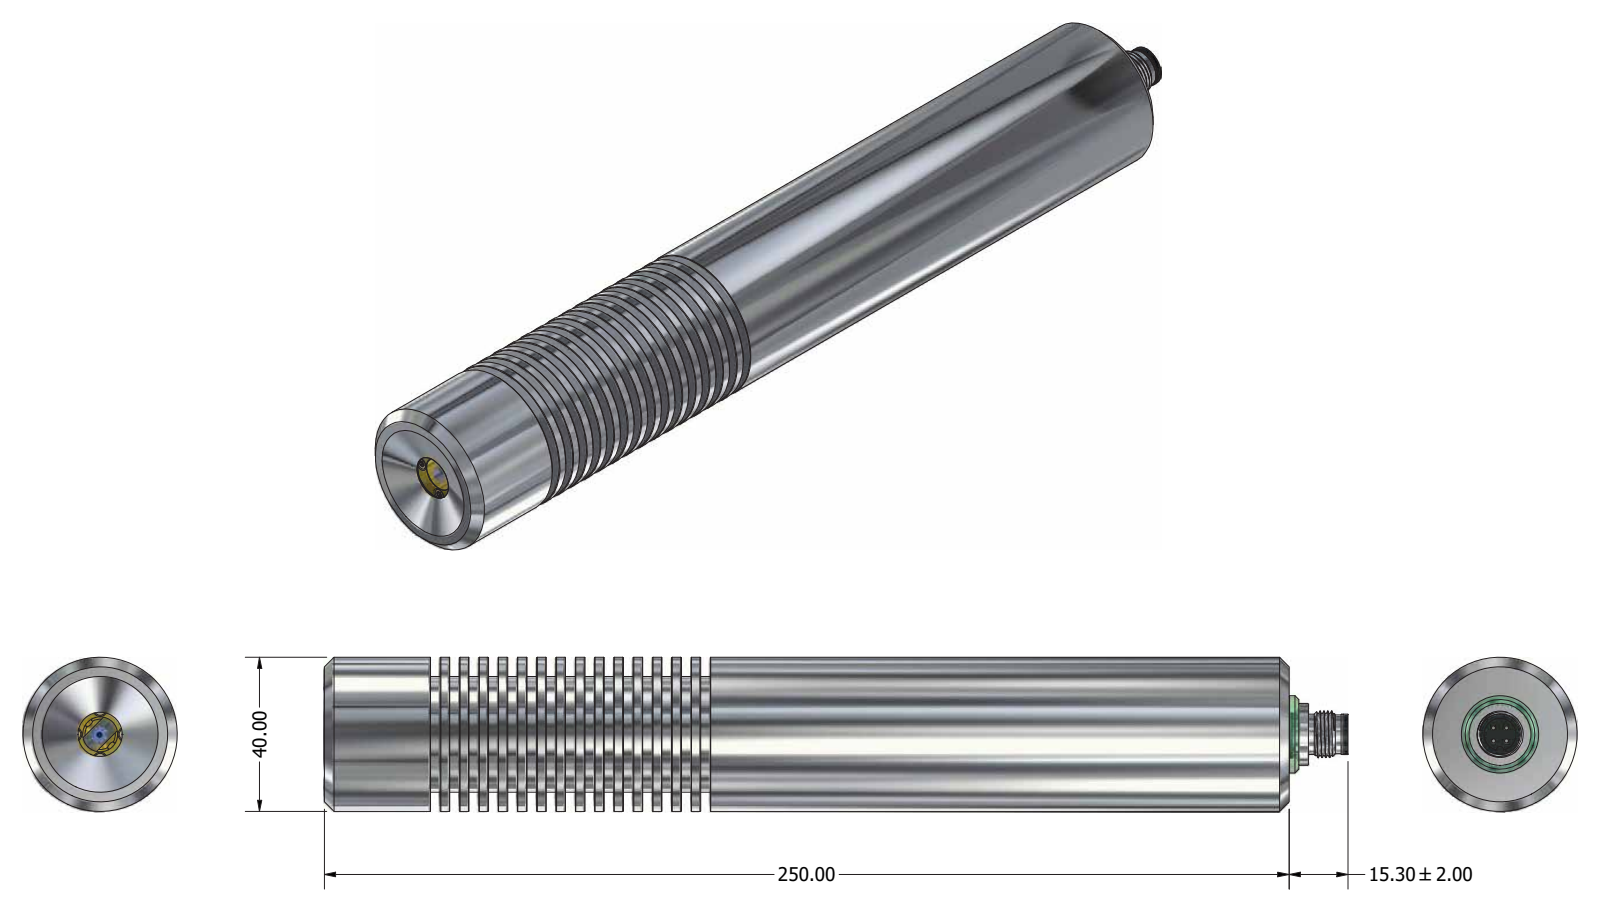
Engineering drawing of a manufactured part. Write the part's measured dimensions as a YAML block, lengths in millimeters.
part_name: "lwpro40; back_40mm_heatsink_rev2; front_40mm_heatsink_rev2; m12_4p_realthread (+1 more)"
step_written_by: "unknown (AUTOMOTIVE_DESIGN)"
units: millimeters
bodies: {solids: 4, faces: 205, planar: 50, cylindrical: 76, other: 79}
overall_size: [265.3, 40, 40]
volume: 242918
surface_area: 64924
round_holes:
  - {diameter: 0.75, count: 4}
  - {diameter: 8.2, count: 1}
  - {diameter: 10.92, count: 1}
  - {diameter: 11.5, count: 1}
  - {diameter: 16, count: 1}
  - {diameter: 16.1, count: 1}
  - {diameter: 16.92, count: 1}
  - {diameter: 17.46, count: 1}
  - {diameter: 18, count: 1}
  - {diameter: 18.4, count: 1}
  - {diameter: 27, count: 1}
round_bosses_or_shafts:
  - {diameter: 1.5, count: 4}
  - {diameter: 1, count: 4}
  - {diameter: 40, count: 1}
  - {diameter: 30, count: 1}
  - {diameter: 23, count: 1}
  - {diameter: 20, count: 1}
  - {diameter: 16.5, count: 1}
  - {diameter: 12, count: 1}
partial_cylinders:
  - {radius: 4.54, count: 4}
  - {radius: 0.9, count: 1}
face_to_face_distances: [5, 10, 15, 20, 25, 30, 35, 40, 2.5, 45]
hole_center_spacings: [2.5, 3.54, 5]
